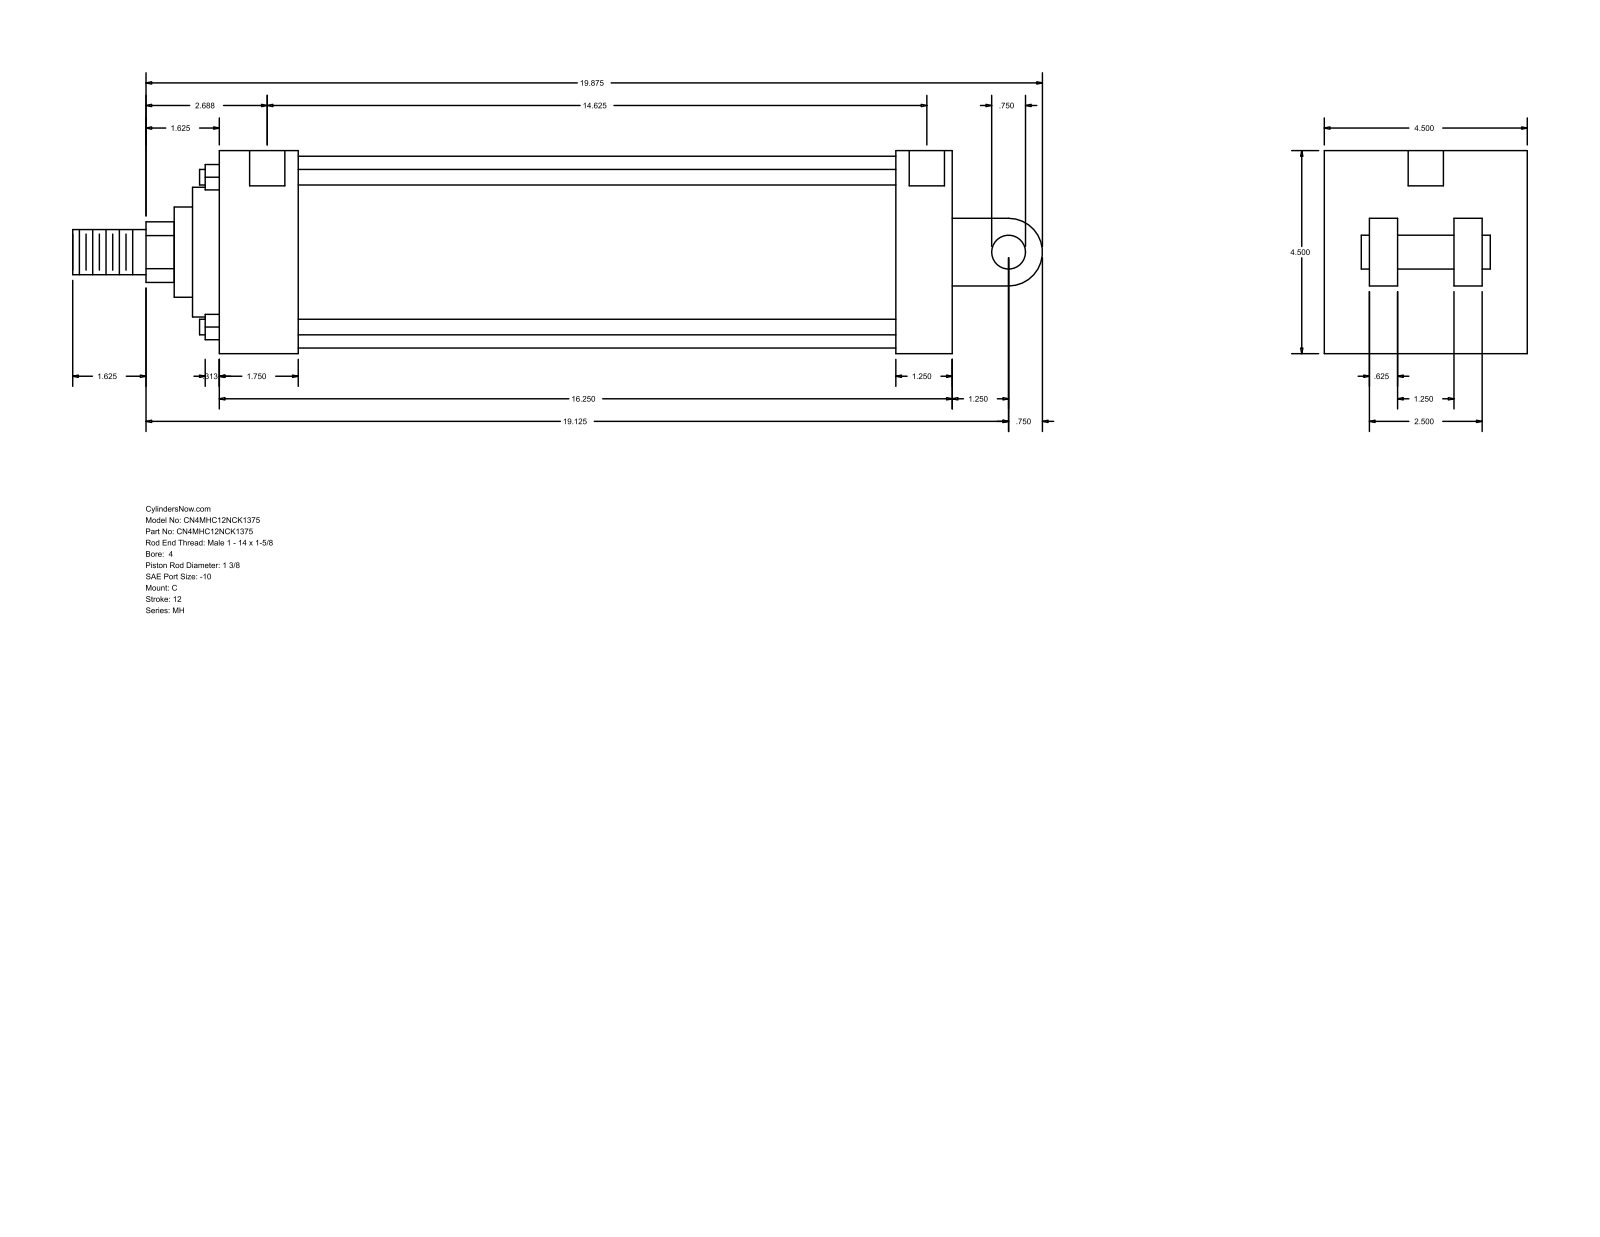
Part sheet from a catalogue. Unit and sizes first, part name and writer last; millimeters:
Units: millimetres
Overall size (bounding box): 546.1 × 114.3 × 114.3
Round holes (diameter × count): ⌀8.73 ×4, ⌀19.84 ×2
Round bosses / shafts (diameter × count): ⌀8.76 ×4, ⌀107.95 ×1, ⌀73.03 ×1, ⌀50.8 ×1, ⌀34.92 ×1, ⌀25.4 ×1, ⌀19.05 ×1
Partial cylindrical surfaces — rounded edges, fillets, slot ends (radius × count): R17.06 ×1, R19.05 ×1
Main face-to-face distances: 114.3, 412.75, 44.45, 381, 336.55, 368.3, 31.75, 41.27, 73.03, 38.1
Hole centre spacings: 374.65, 1.58, 1.59, 371.48, 373.06, 373.07
Bodies: 0 solids, 101 faces (71 planar, 30 cylindrical, 0 other)
Part name (STEP PRODUCT): MH_C__0400_1.375
STEP written by: GSSL Pune (CONFIG_CONTROL_DESIGN)
